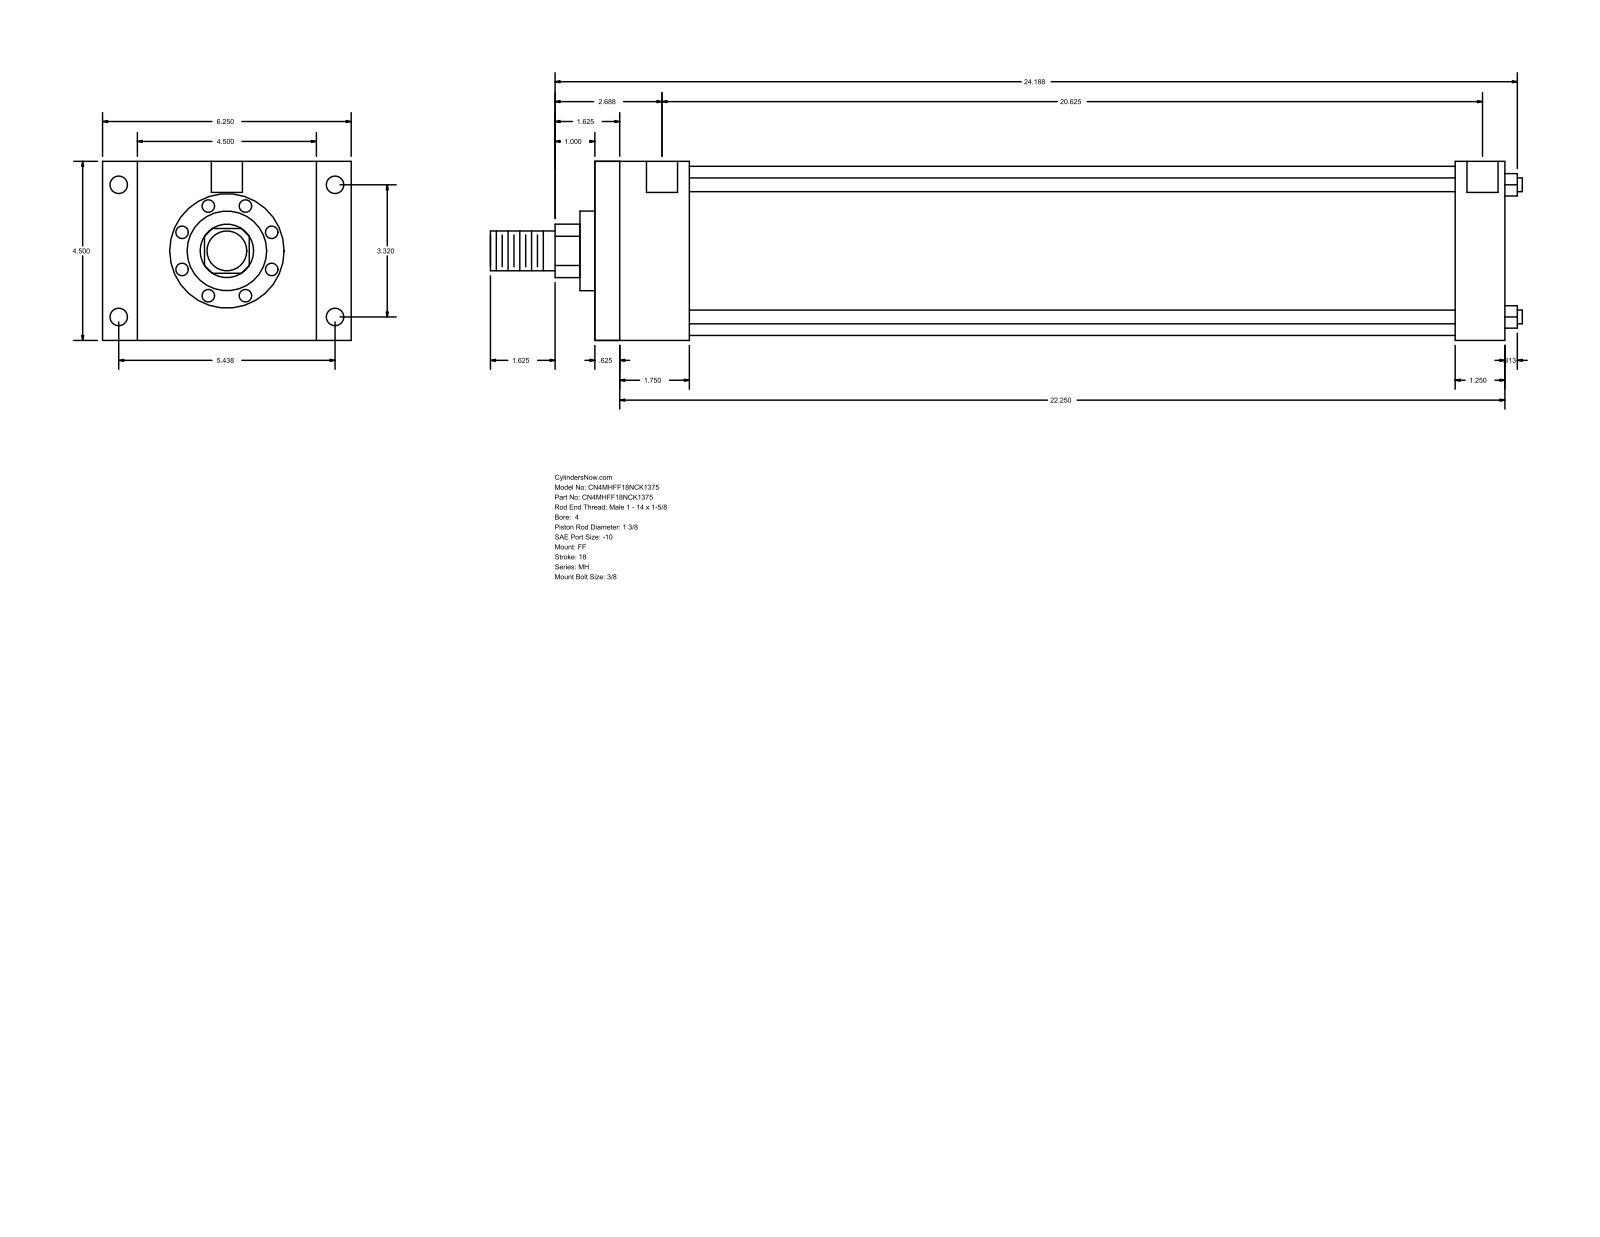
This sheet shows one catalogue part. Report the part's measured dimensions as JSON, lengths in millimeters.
{"part_name": "MH_FF__0400_1.375", "step_written_by": "GSSL Pune (CONFIG_CONTROL_DESIGN)", "units": "millimeters", "bodies": {"solids": 0, "faces": 92, "planar": 64, "cylindrical": 28, "other": 0}, "overall_size": [658.81, 158.75, 114.3], "round_holes": [[8.73, 4], [11.13, 4], [19.84, 2]], "round_bosses_or_shafts": [[8.76, 4], [107.95, 1], [50.8, 1], [34.92, 1], [25.4, 1]], "partial_cylinders_radius": [[17.06, 1]], "face_to_face_distances": [114.3, 581.02, 15.87, 565.15, 60.32, 44.45, 520.7, 549.27, 533.4, 488.95], "hole_center_spacings": [1.59, 84.32, 138.12, 161.82, 525.47, 527.06, 523.88]}
